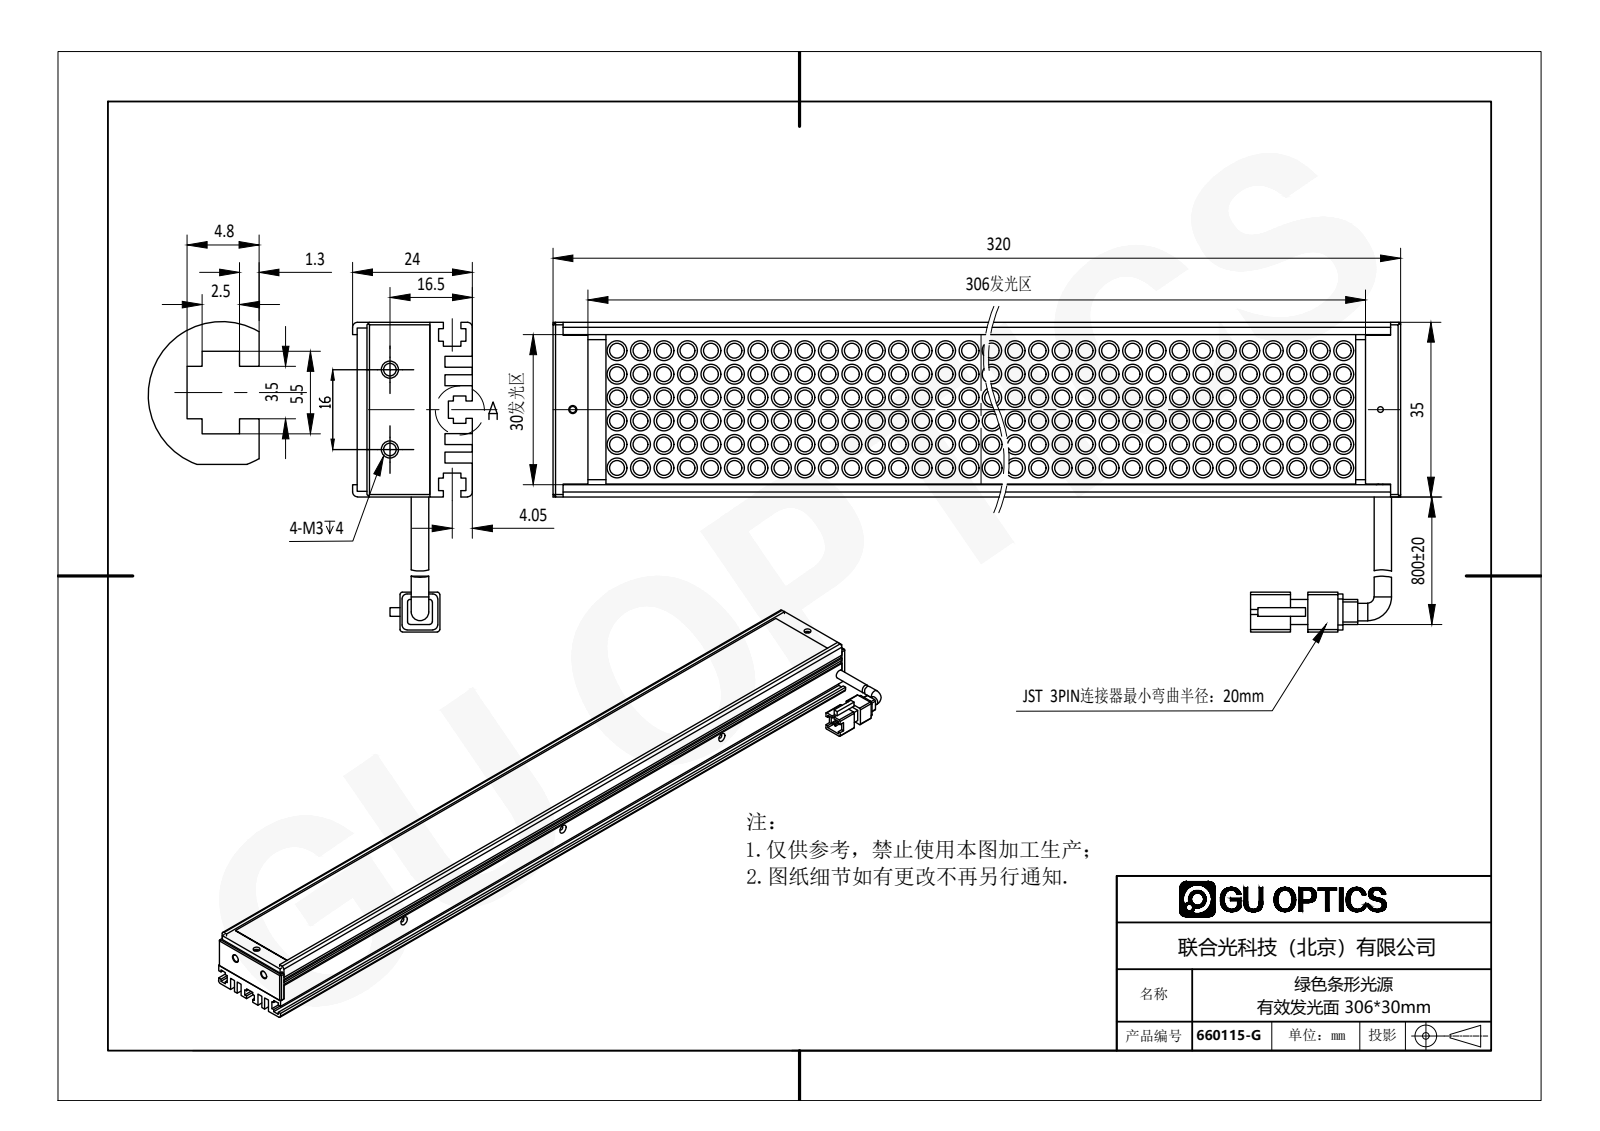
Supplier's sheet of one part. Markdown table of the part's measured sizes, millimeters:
| quantity | value |
| --- | --- |
| part name | 660115-G |
| STEP written by | SolidWorks 2016 (AUTOMOTIVE_DESIGN) |
| units | millimeters |
| bodies | 11 solids, 2871 faces (733 planar, 1647 cylindrical, 491 other) |
| overall size | 320 × 62 × 24 |
| volume | 140 705 mm³ |
| surface area | 161 979 mm² |
| round holes (diameter × count) | 1.6 × 5, 1.7 × 3, 1.5 × 2, 2.5 × 2, 2.8 × 2, 3 × 2, 1.1 × 1, 1.25 × 1, 2 × 1 |
| round bosses / shafts (diameter × count) | 4 × 384, 3 × 384, 3.5 × 2 |
| partial cylindrical surfaces (radius × count) | 1 × 28, 0.5 × 8, 1.65 × 1 |
| main face-to-face distances | 2, 2.2, 11.2, 1, 2.5, 12.6, 14.6, 9.2, 14.8, 8.5 |
| hole center spacings | 312, 7, 66.02, 66.22, 90, 156.01, 156.09, 246.01 |
